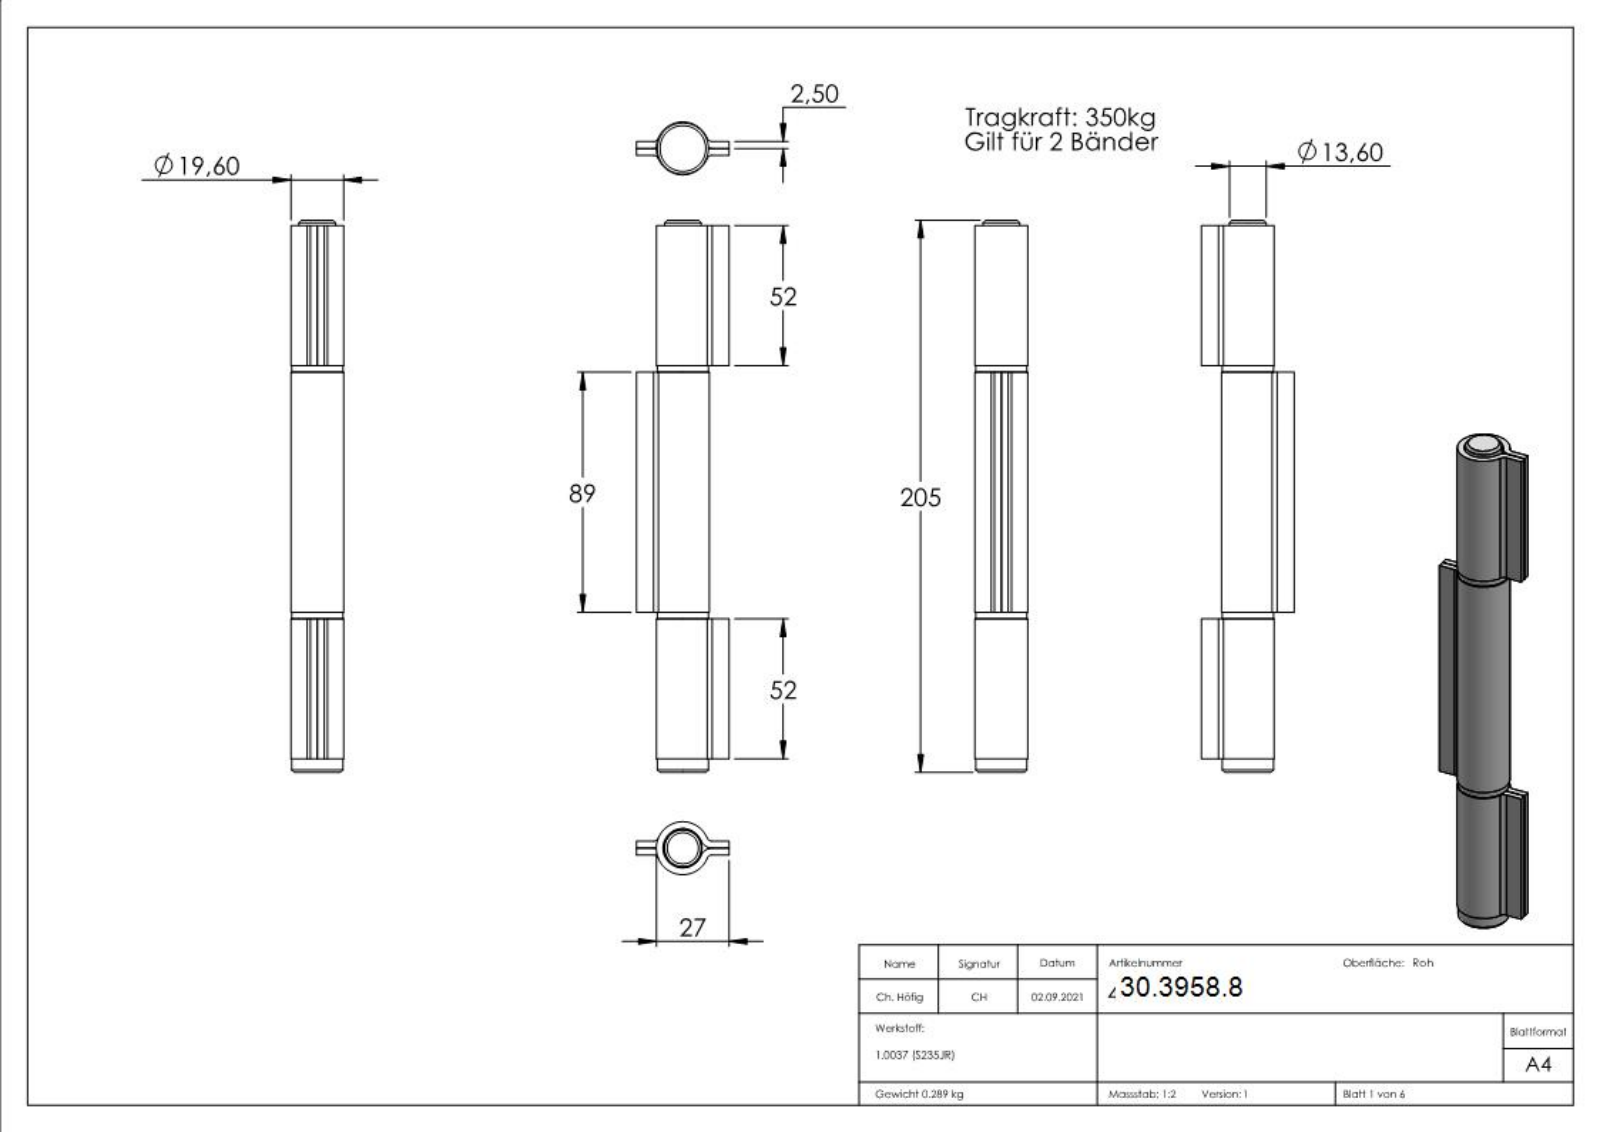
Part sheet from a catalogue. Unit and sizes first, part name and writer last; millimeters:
Units: millimetres
Overall size (bounding box): 205 × 34.4 × 19.6
Round holes (diameter × count): ⌀14 ×1, ⌀14.6 ×1
Round bosses / shafts (diameter × count): ⌀19.6 ×1, ⌀19 ×1, ⌀13.6 ×1
Partial cylindrical surfaces — rounded edges, fillets, slot ends (radius × count): R2 ×4, R4.5 ×4, R7.4 ×1
Main face-to-face distances: 2.5, 2.6, 5.1, 91.5, 52, 146, 143.5, 54.5, 34.4, 94
Volume: 63 499 mm³ · Surface area: 38 296 mm²
Bodies: 6 solids, 287 faces (142 planar, 44 cylindrical, 101 other)
Part name (STEP PRODUCT): 415-xx Teil1_415-20 Teil1; 415-xx Teil2_415-20 Teil2; 415-xx Teil2; 415-xx Teil4_415-20 Teil4 (+5 more)
STEP written by: SolidWorks 2018 (CONFIG_CONTROL_DESIGN)
